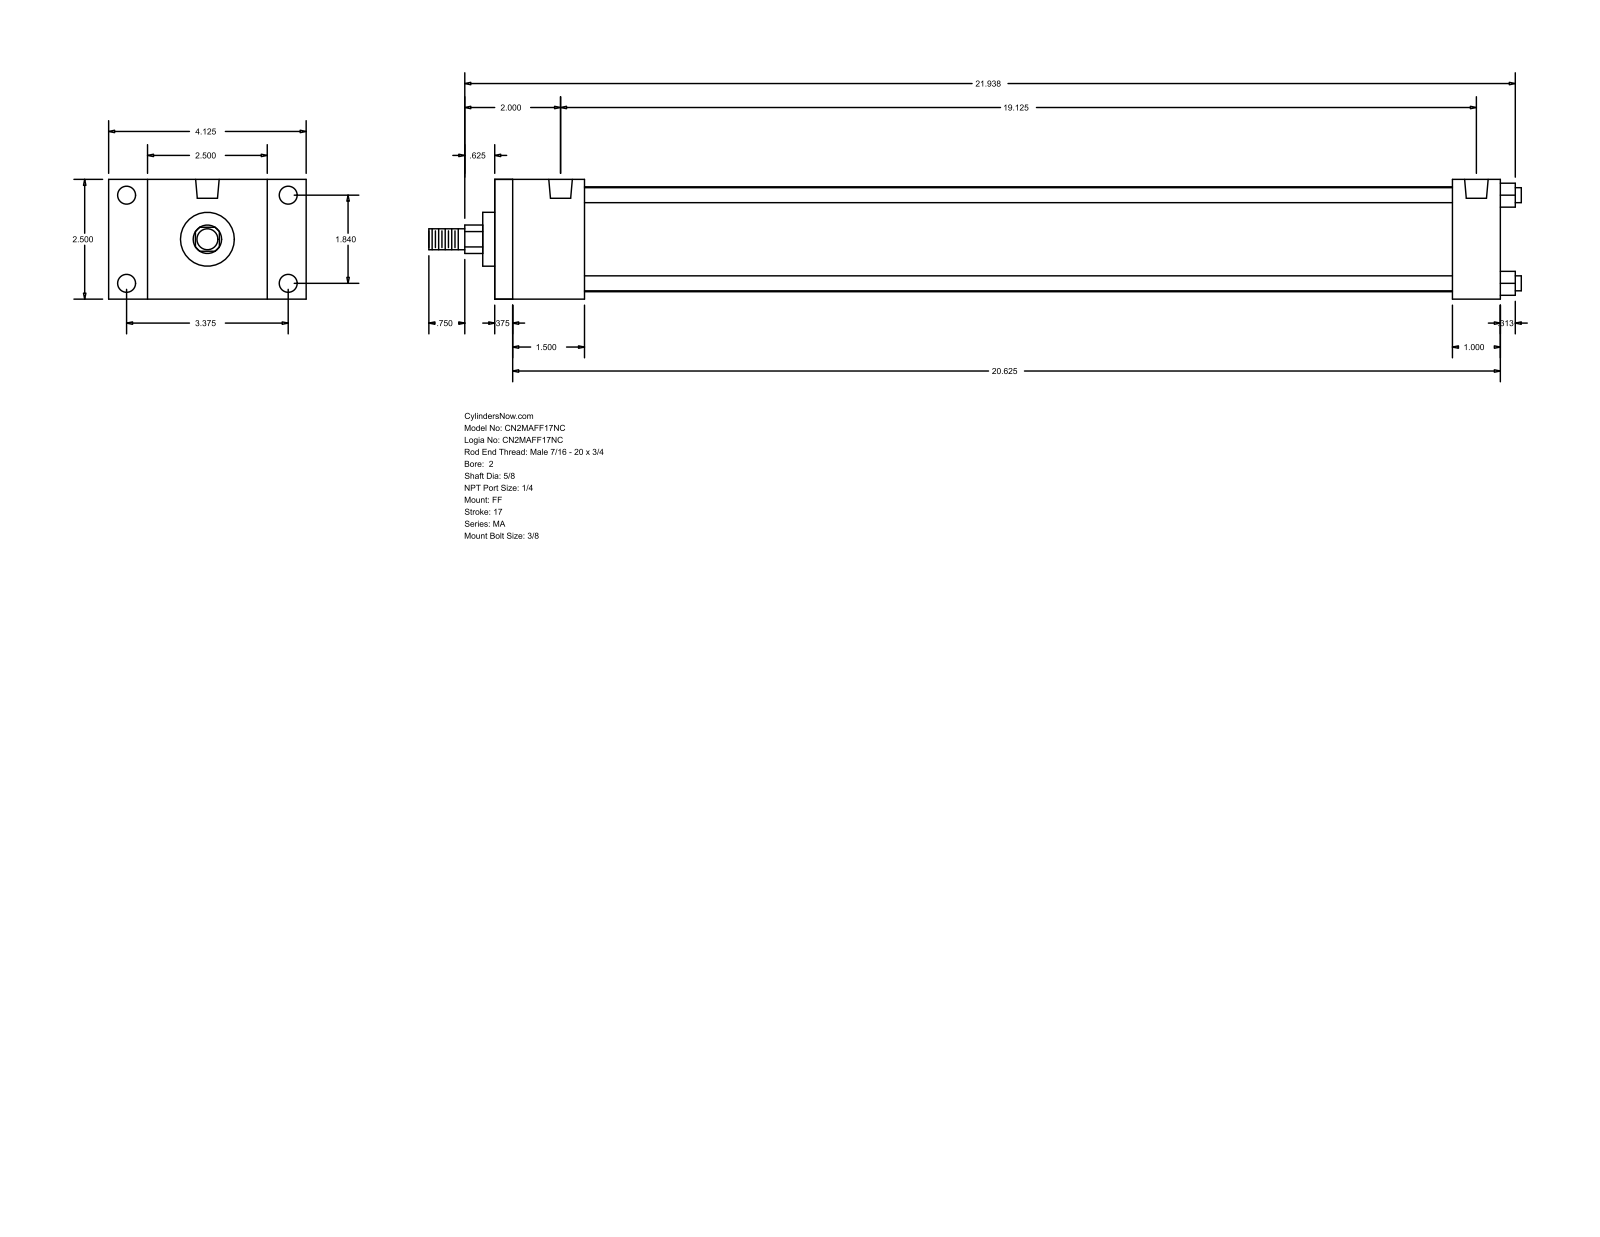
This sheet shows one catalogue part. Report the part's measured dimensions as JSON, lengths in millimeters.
{"part_name": "MA_FF__0200_0.625", "step_written_by": "GSSL Pune (CONFIG_CONTROL_DESIGN)", "units": "millimeters", "bodies": {"solids": 0, "faces": 92, "planar": 64, "cylindrical": 28, "other": 0}, "overall_size": [579.44, 104.78, 63.5], "round_holes": [[7.94, 4], [9.53, 4], [12.49, 2]], "round_bosses_or_shafts": [[7.94, 4], [55.63, 1], [28.57, 1], [15.88, 1], [11.11, 1]], "partial_cylinders_radius": [[7.54, 1]], "face_to_face_distances": [63.5, 533.39, 9.52, 523.87, 38.1, 47.62, 508, 498.48, 460.38, 485.77], "hole_center_spacings": [46.74, 85.72, 97.63, 485.78]}
